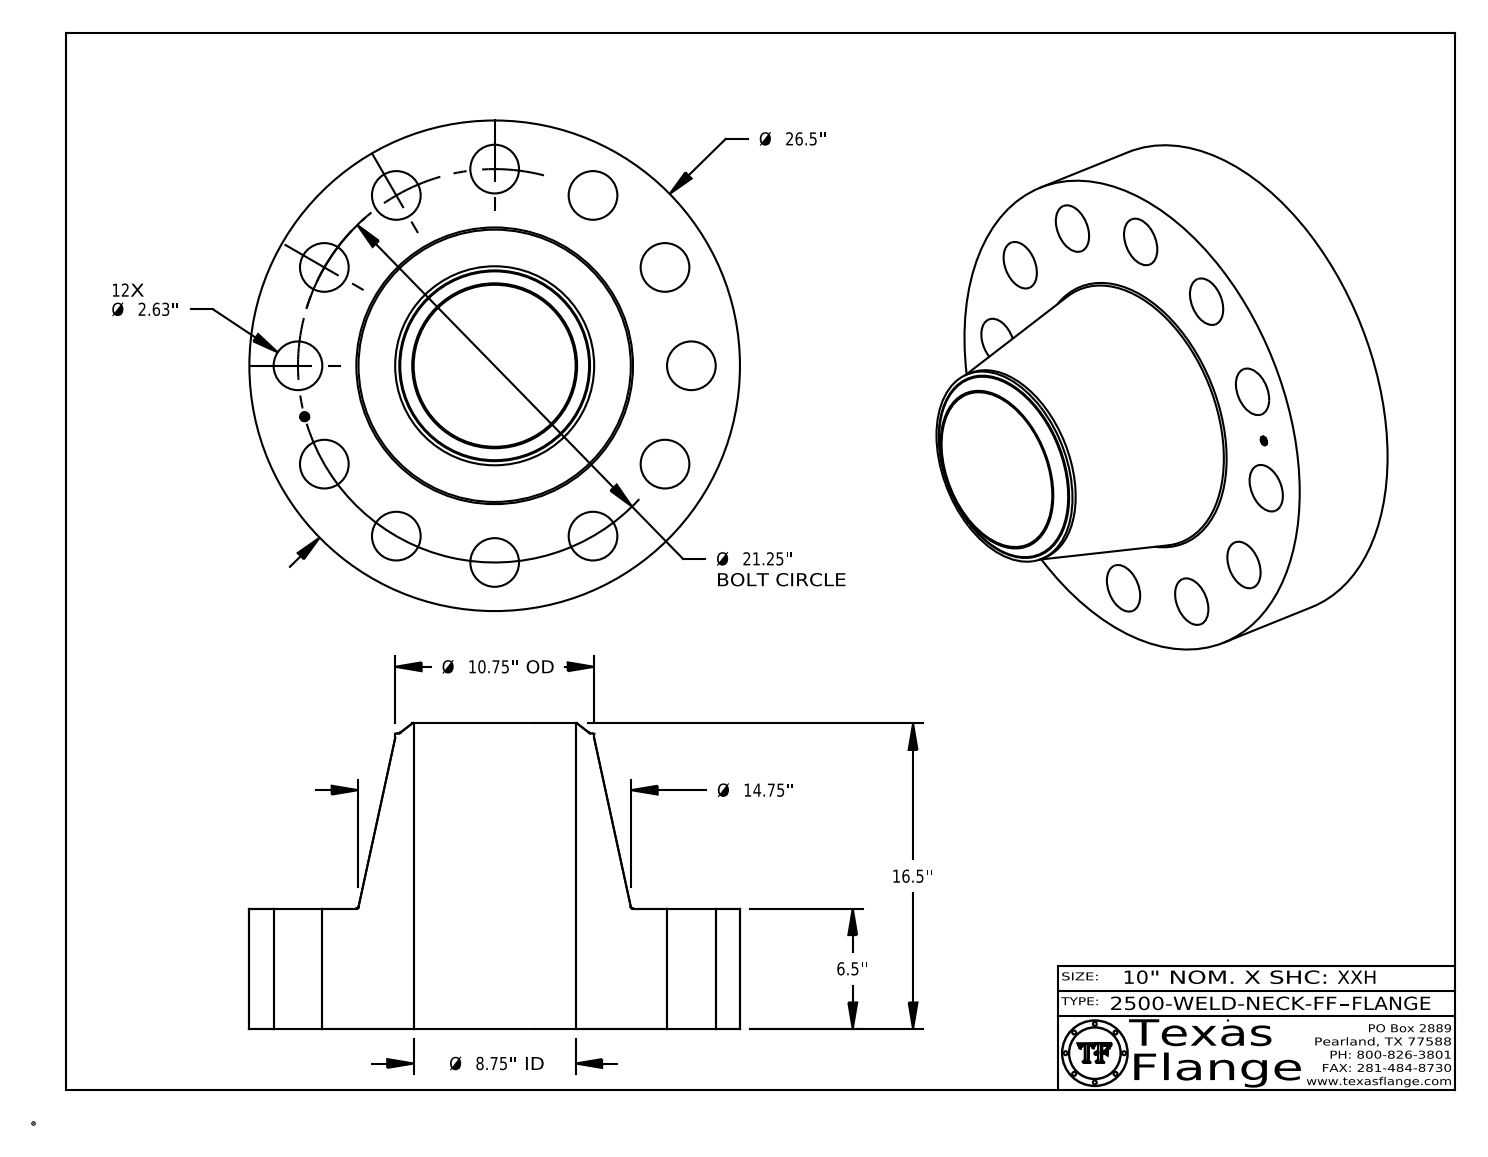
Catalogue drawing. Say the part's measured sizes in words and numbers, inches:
The part is named "2500-WELD-NECK-FF". Its 3-D file was written by "CATIA V5 STEP AP214 (AUTOMOTIVE_DESIGN)". It is 1 solid with 428 faces: 368 planar, 50 cylindrical and 10 other. Overall it measures 26.5 by 26.5 by 16.5 inches. Its volume is 3 417 cubic inches and its surface area 2 801 square inches. Round holes: 12 of diameter 2.63, 1 of diameter 0.495, 1 of diameter 8.75. Round bosses or shafts: 8 of diameter 0.03, 1 of diameter 26.5, 1 of diameter 10.75, 1 of diameter 0.39. The main face-to-face distances are 6.5, 16.5, 10, 6.485, 0.015, 10.015, 0.148, 0.144, 0.027, 0.096. The hole center spacings are 10.625, 5.5, 18.403, 15.026, 20.526, 15.026, 20.526, 21.25.
